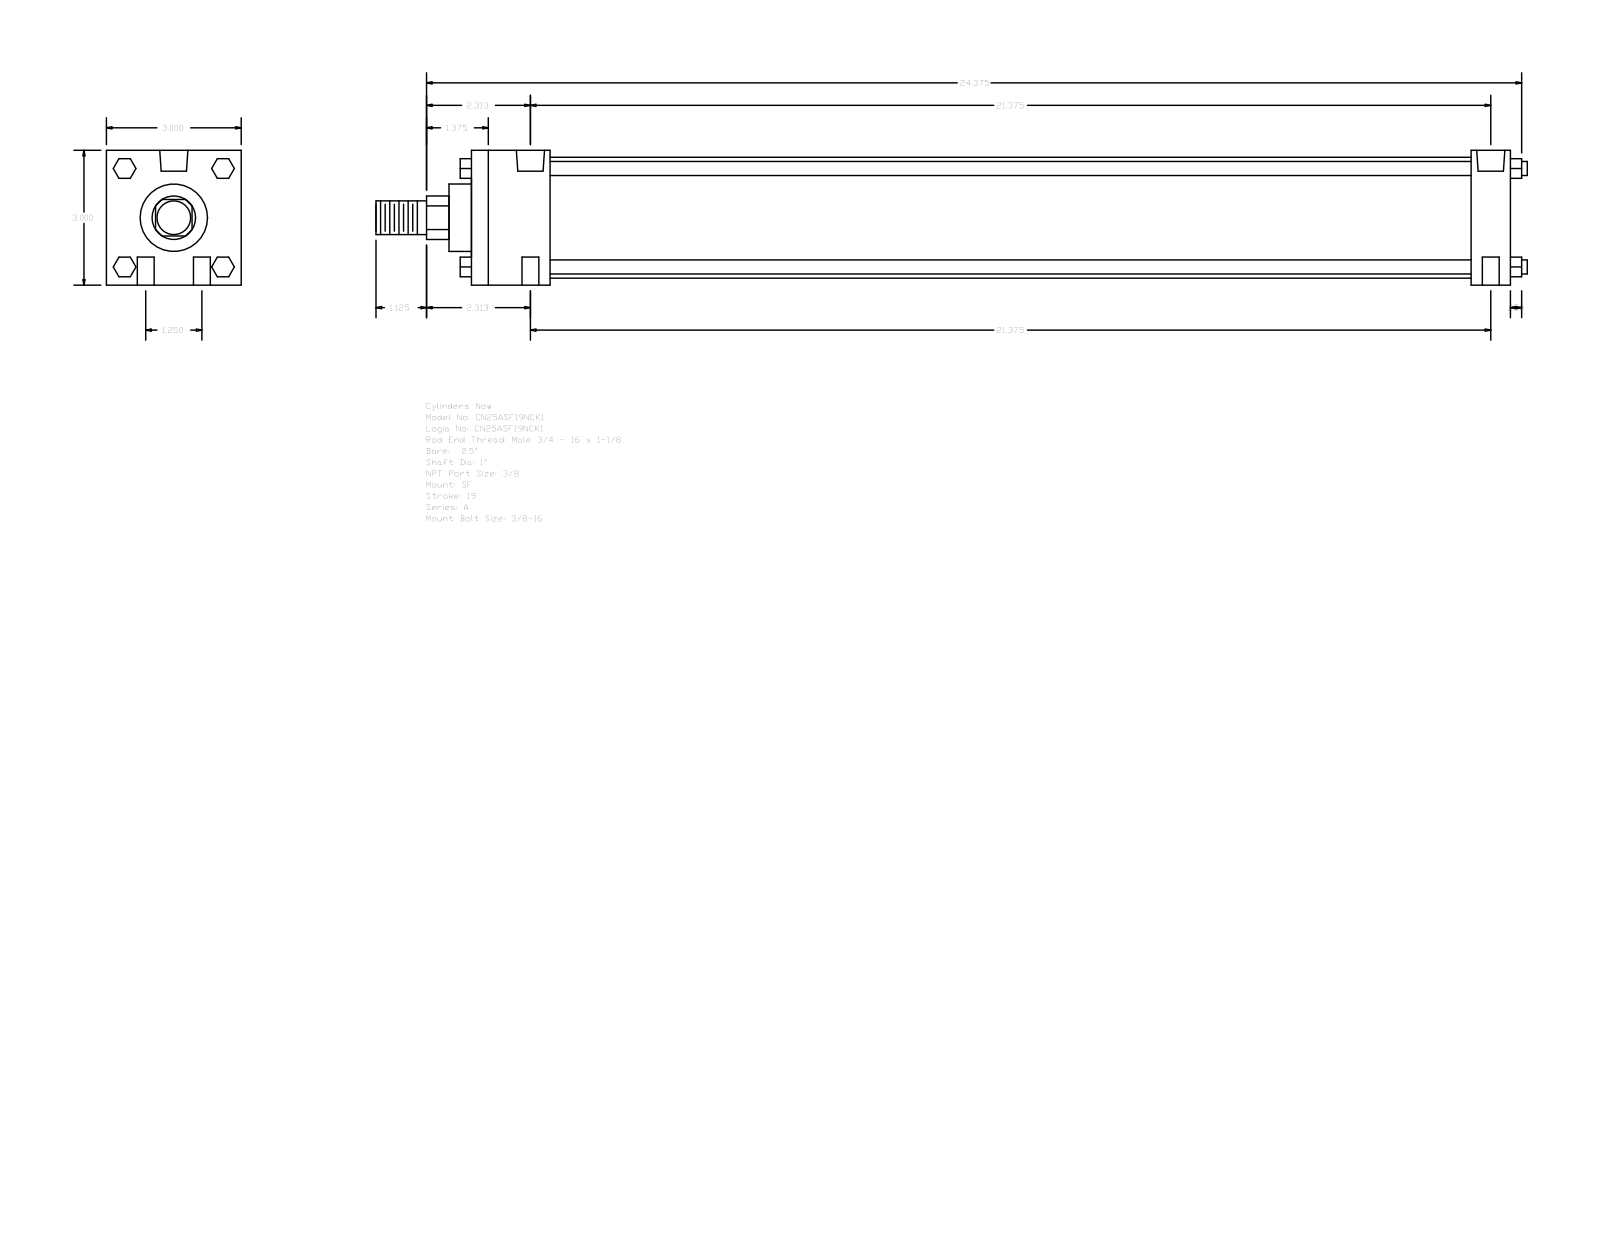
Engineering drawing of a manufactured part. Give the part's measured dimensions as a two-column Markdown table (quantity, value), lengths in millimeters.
| quantity | value |
| --- | --- |
| part name | A_SF__0250_1 |
| STEP written by | GSSL Pune (CONFIG_CONTROL_DESIGN) |
| units | millimeters |
| bodies | 0 solids, 124 faces (94 planar, 30 cylindrical, 0 other) |
| overall size | 650.88 × 76.2 × 76.2 |
| round holes (diameter × count) | 9.53 × 4, 5.56 × 2, 15.93 × 2 |
| round bosses / shafts (diameter × count) | 7.94 × 4, 68.33 × 1, 38.1 × 1, 25.4 × 1, 19.05 × 1 |
| partial cylindrical surfaces (radius × count) | 12.29 × 1 |
| main face-to-face distances | 76.2, 587.37, 565.15, 22.22, 44.45, 520.7, 542.92, 12.7, 600.07, 6.35 |
| hole center spacings | 15.88, 543.15, 542.92, 31.76, 543.85, 547.68 |
